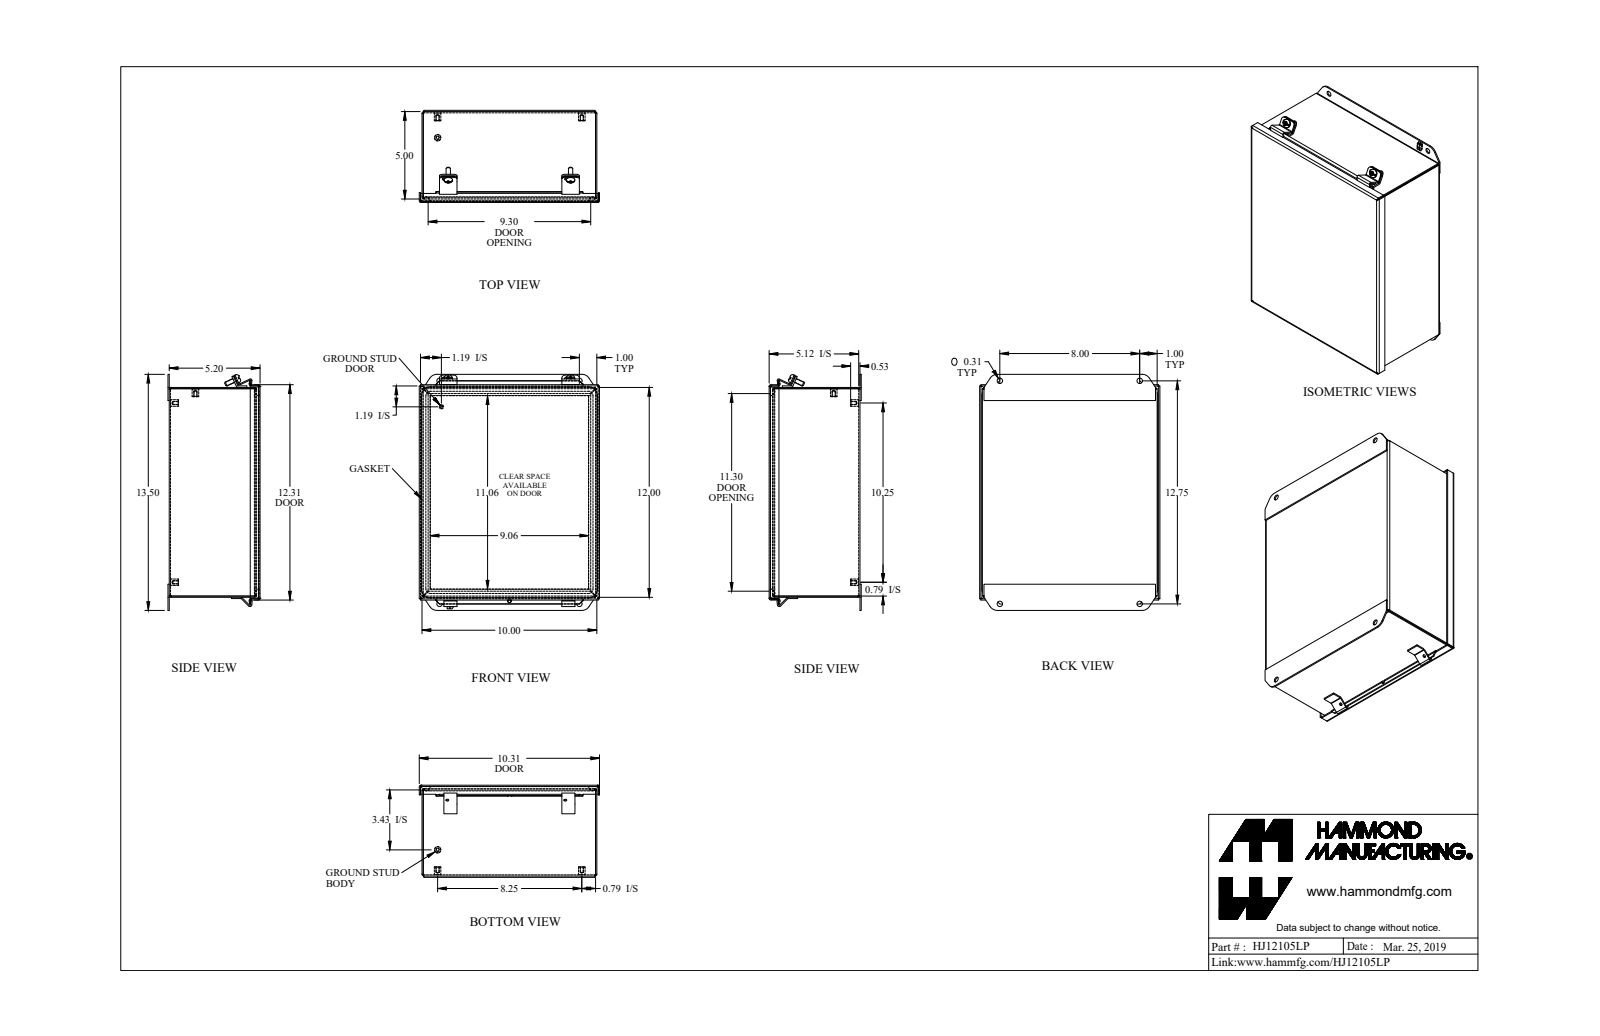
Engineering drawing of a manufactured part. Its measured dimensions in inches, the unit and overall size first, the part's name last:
Units: inches
Overall size (bounding box): 13.5 × 10.312 × 5.269
Round holes (diameter × count): ⌀0.156 ×5, ⌀0.313 ×4, ⌀0.156 ×2, ⌀0.213 ×2
Round bosses / shafts (diameter × count): ⌀0.375 ×5, ⌀0.25 ×3, ⌀0.48 ×2, ⌀0.188 ×1
Partial cylindrical surfaces — rounded edges, fillets, slot ends (radius × count): R0.036 ×16, R0.108 ×16, R0.25 ×16, R0.188 ×8, R0.141 ×4, R0.499 ×4, R0.5 ×4, R0.01 ×2
Main face-to-face distances: 0.072, 5.125, 5.197, 5.053, 9.928, 11.928, 9.856, 10, 12, 11.856
Hole centre spacings: 8, 8.25, 10.25, 12.75, 13.158, 15.052, 1.24, 1.243
Volume: 42.59 in³ · Surface area: 1 179 in²
Bodies: 19 solids, 622 faces (341 planar, 156 cylindrical, 125 other)
Part name (STEP PRODUCT): HJ12105LP
STEP written by: SolidWorks 2018 (AUTOMOTIVE_DESIGN)
